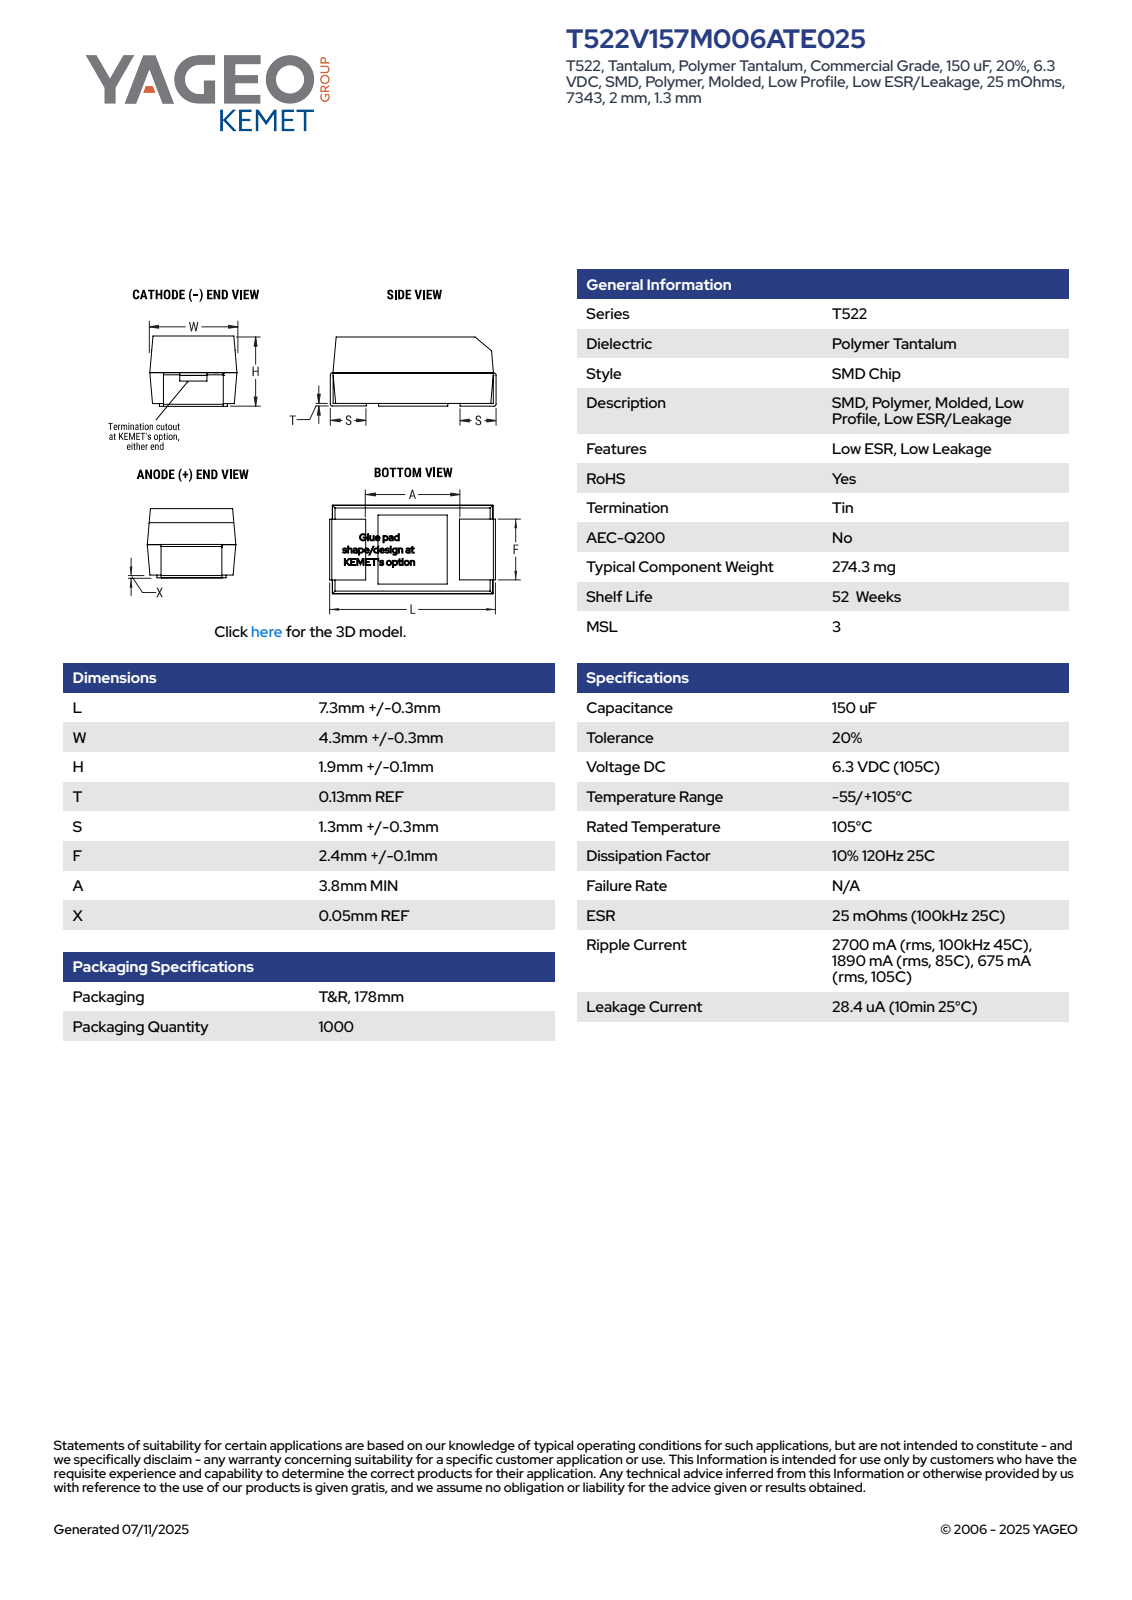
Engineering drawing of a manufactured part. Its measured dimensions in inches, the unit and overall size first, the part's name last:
Units: inches
Overall size (bounding box): 0.299 × 0.181 × 0.084
Partial cylindrical surfaces — rounded edges, fillets, slot ends (radius × count): R0.004 ×4
Main face-to-face distances: 0.079, 0.175, 0.175, 0.084, 0.294, 0.299, 0.289, 0.051, 0.248, 0.046
Volume: 0.004 in³ · Surface area: 0.181 in²
Bodies: 4 solids, 90 faces (86 planar, 4 cylindrical, 0 other)
Part name (STEP PRODUCT): CTSM_TCM2NBKRPEG_7343_L7.6W4.6H2T0.13S1.3F2.5A3.8X0.05
STEP written by: SolidWorks 2014 (AUTOMOTIVE_DESIGN)
